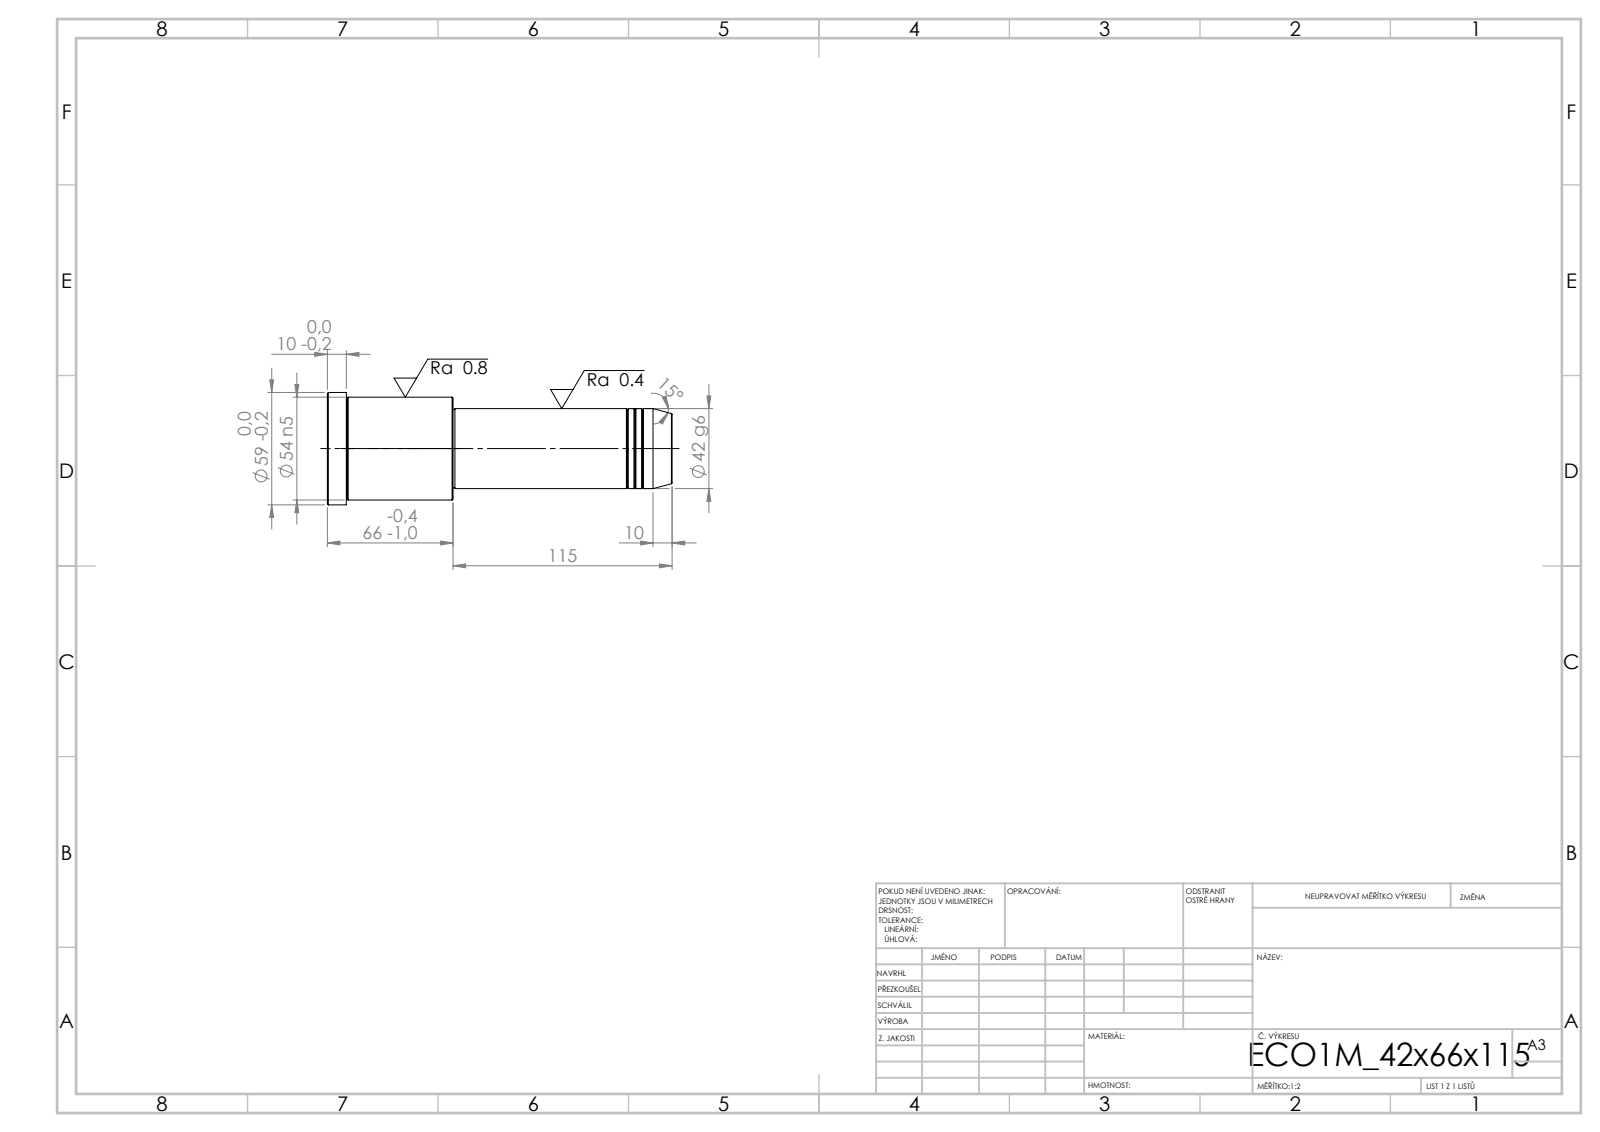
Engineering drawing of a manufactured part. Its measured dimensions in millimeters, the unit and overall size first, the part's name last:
Units: millimetres
Overall size (bounding box): 181 × 59 × 59
Round bosses / shafts (diameter × count): ⌀59 ×1, ⌀54 ×1, ⌀42 ×1, ⌀41 ×1
Main face-to-face distances: 181, 115, 66, 171, 56, 10, 114, 1, 57, 67
Volume: 312 893 mm³ · Surface area: 31 944 mm²
Bodies: 1 solid, 43 faces (5 planar, 14 cylindrical, 24 other)
STEP written by: SolidWorks 2019 (CONFIG_CONTROL_DESIGN)
